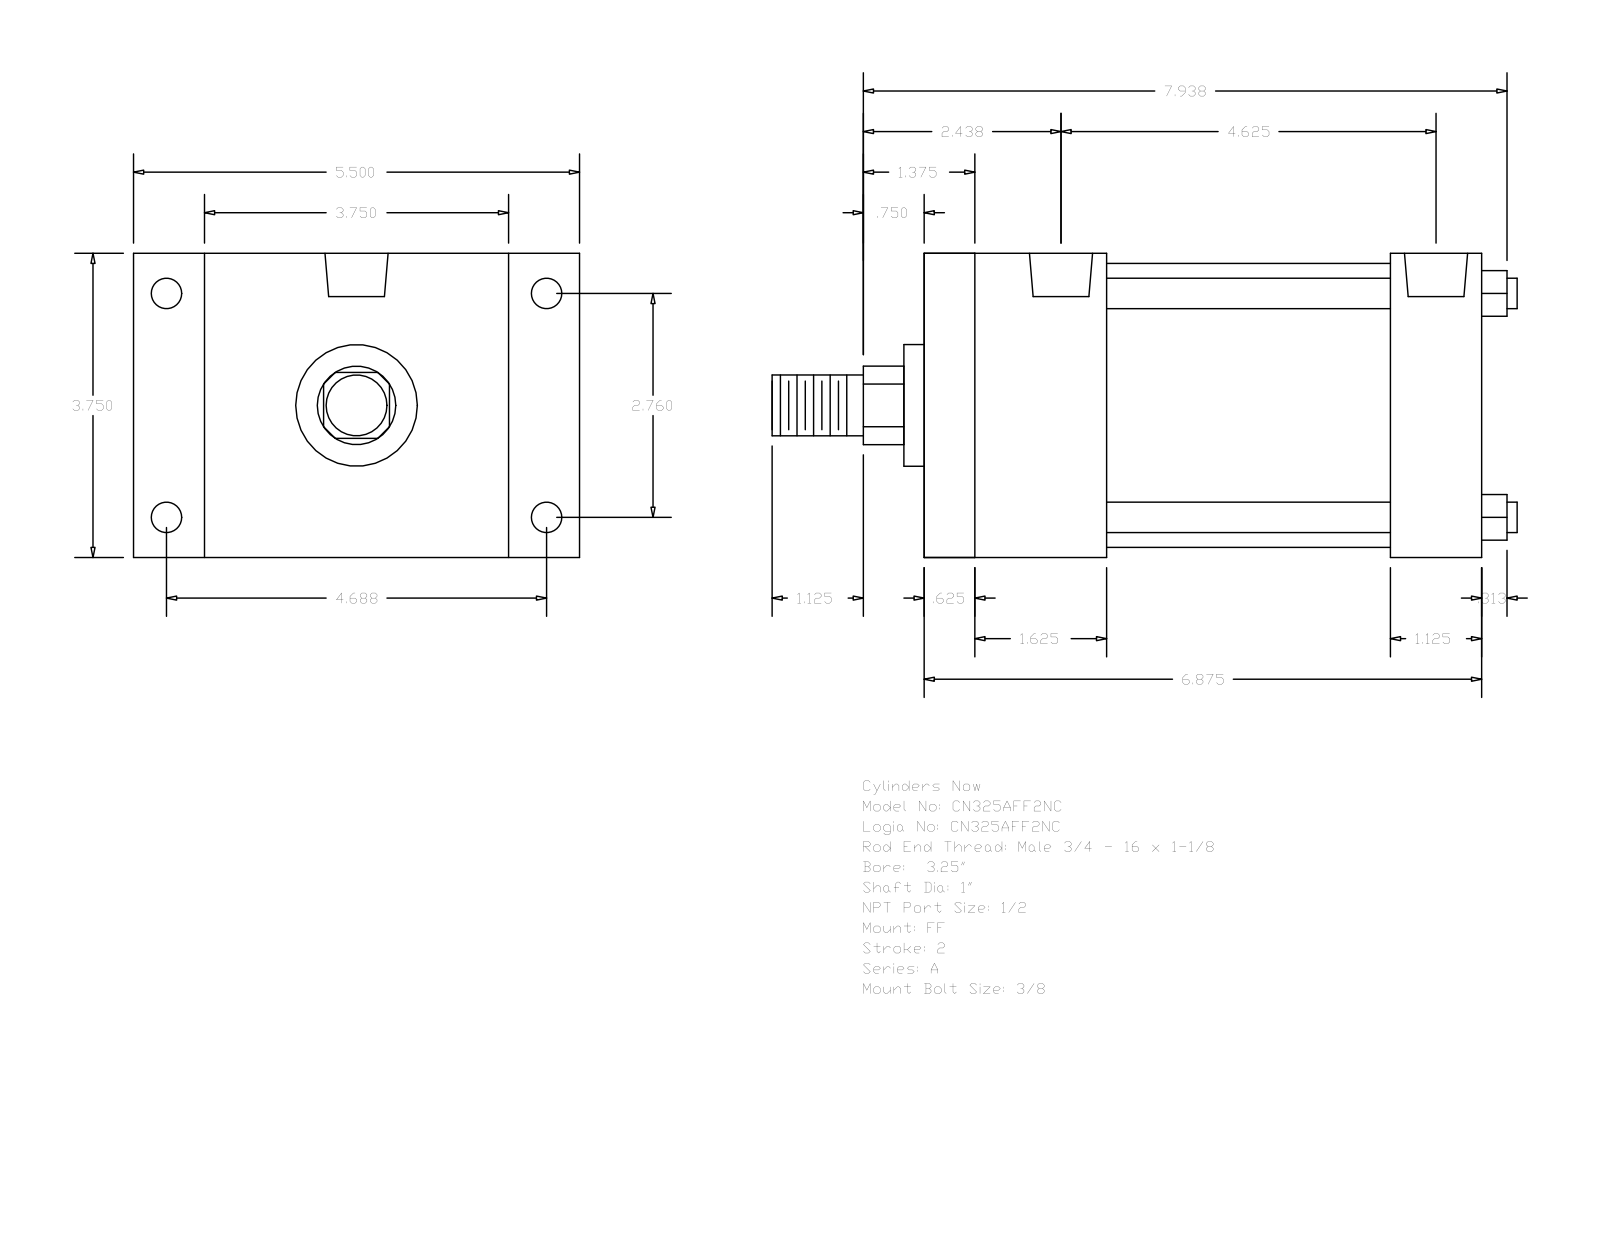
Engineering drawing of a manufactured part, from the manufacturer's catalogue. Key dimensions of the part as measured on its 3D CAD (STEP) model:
Part name (STEP PRODUCT): A_FF__0325_1
STEP written by: GSSL Pune (CONFIG_CONTROL_DESIGN)
Units: millimetres
Bodies: 0 solids, 92 faces (64 planar, 28 cylindrical, 0 other)
Overall size (bounding box): 233.36 × 139.7 × 95.25
Round holes (diameter × count): ⌀8.73 ×4, ⌀9.53 ×4, ⌀19.77 ×2
Round bosses / shafts (diameter × count): ⌀9.53 ×4, ⌀88.9 ×1, ⌀38.1 ×1, ⌀25.4 ×1, ⌀19.05 ×1
Partial cylindrical surfaces — rounded edges, fillets, slot ends (radius × count): R12.29 ×1
Main face-to-face distances: 95.24, 174.63, 15.87, 158.76, 22.23, 117.47, 57.15, 146.05, 41.28, 130.18
Hole centre spacings: 3.18, 70.1, 111.12, 114.3, 119.06, 138.16, 117.48
